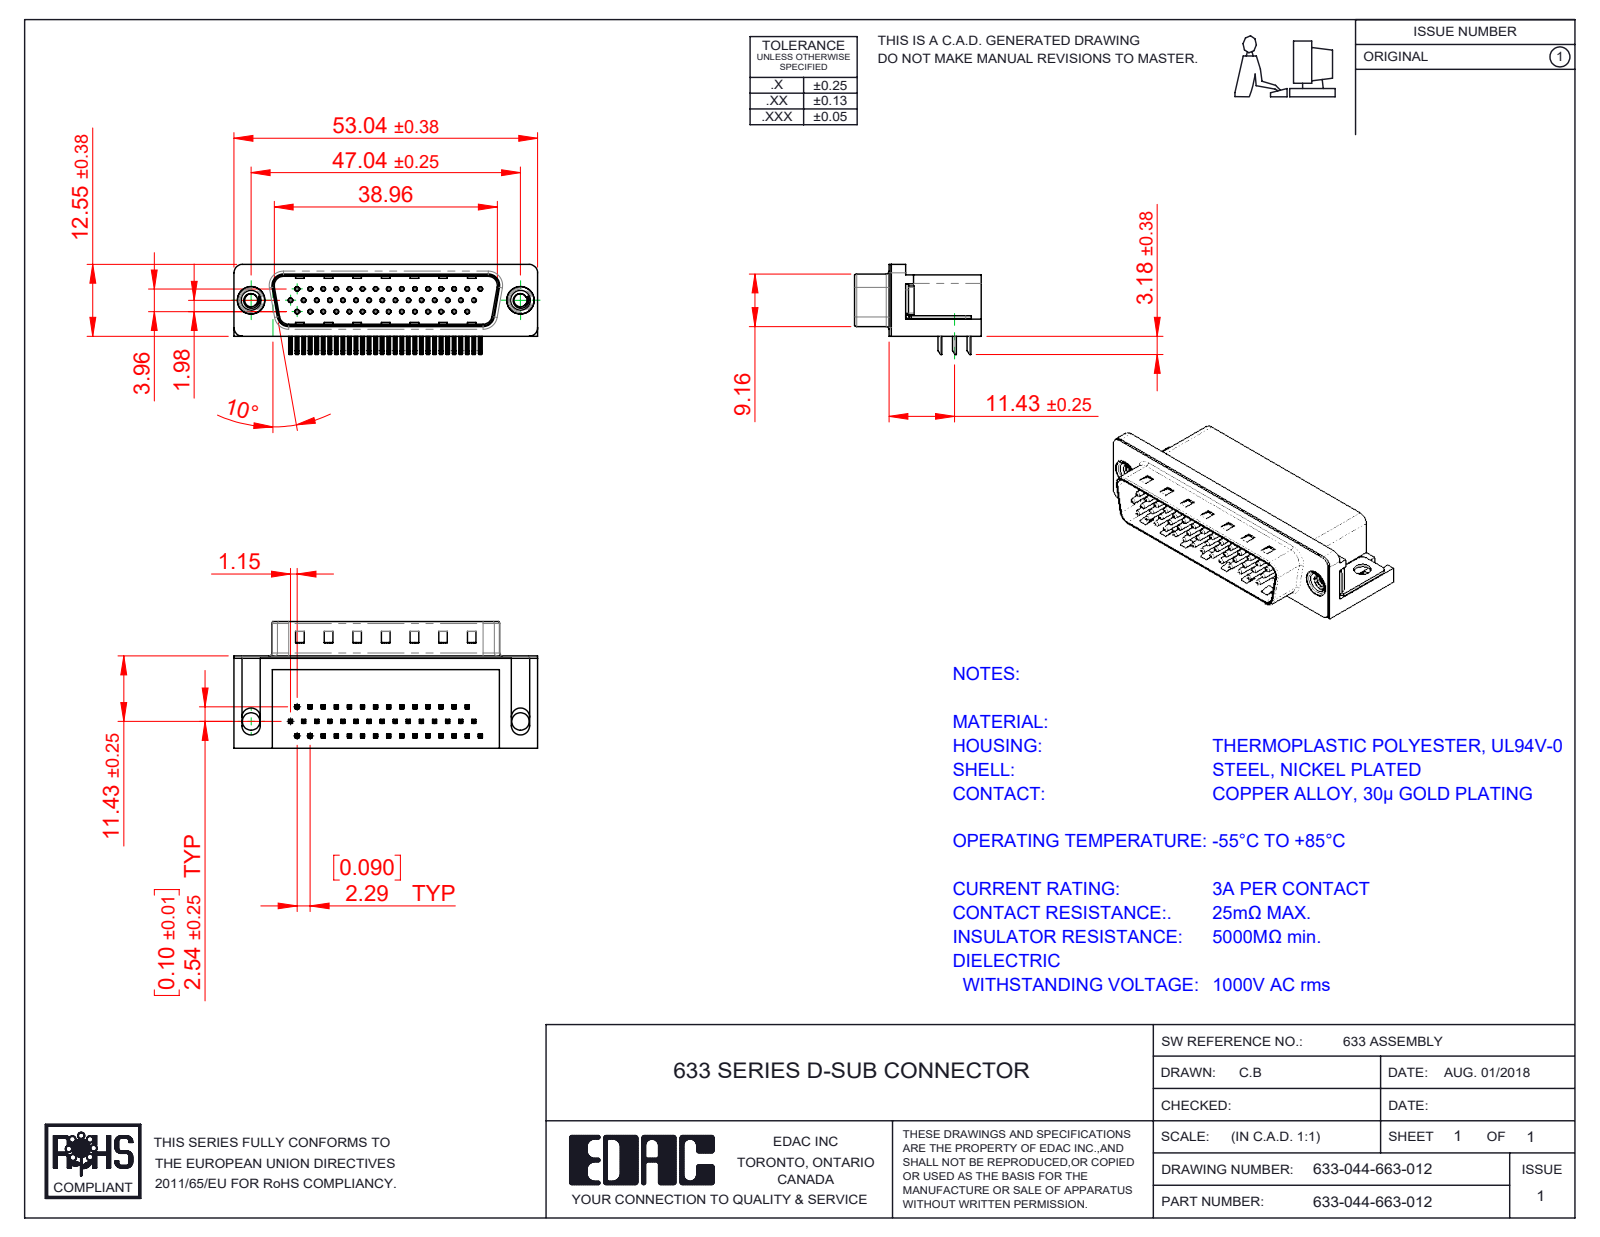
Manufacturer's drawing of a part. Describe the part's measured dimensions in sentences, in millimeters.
The part is named "633 Housing_44 Contact; 633 Contact Top; 633 4-40 Threaded Rivet; 633 Contact Bottom (+4 more)". Its 3-D file was written by "SolidWorks 2016 (CONFIG_CONTROL_DESIGN)". It is 50 solids with 3688 faces: 2315 planar, 1060 cylindrical and 313 other. Overall it measures 53.04 by 22.1 by 15.73 millimeters. Its volume is 8 114 cubic millimeters and its surface area 10 206 square millimeters. Round holes: 44 of diameter 0.35, 44 of diameter 0.8, 2 of diameter 2.26, 2 of diameter 3.05, 2 of diameter 4, 2 of diameter 4.8, 2 of diameter 5. Round bosses or shafts: 44 of diameter 0.75, 2 of diameter 4.9, 2 of diameter 4.75, 2 of diameter 3.9. Partial cylindrical surfaces (rounded edges, fillets, slot ends): 184 of radius 0.25, 88 of radius 0.12, 16 of radius 1, 9 of radius 0.5, 8 of radius 1.6, 7 of radius 1.5, 4 of radius 0.9, 4 of radius 2. The main face-to-face distances are 0.4, 10.35, 15.7, 2.9, 8.76, 2.5, 2.1, 16.1, 10.7, 2.54. The hole center spacings are 2.29, 4.57, 4.58, 2.28, 6.87, 9.16, 11.45, 2.27.
